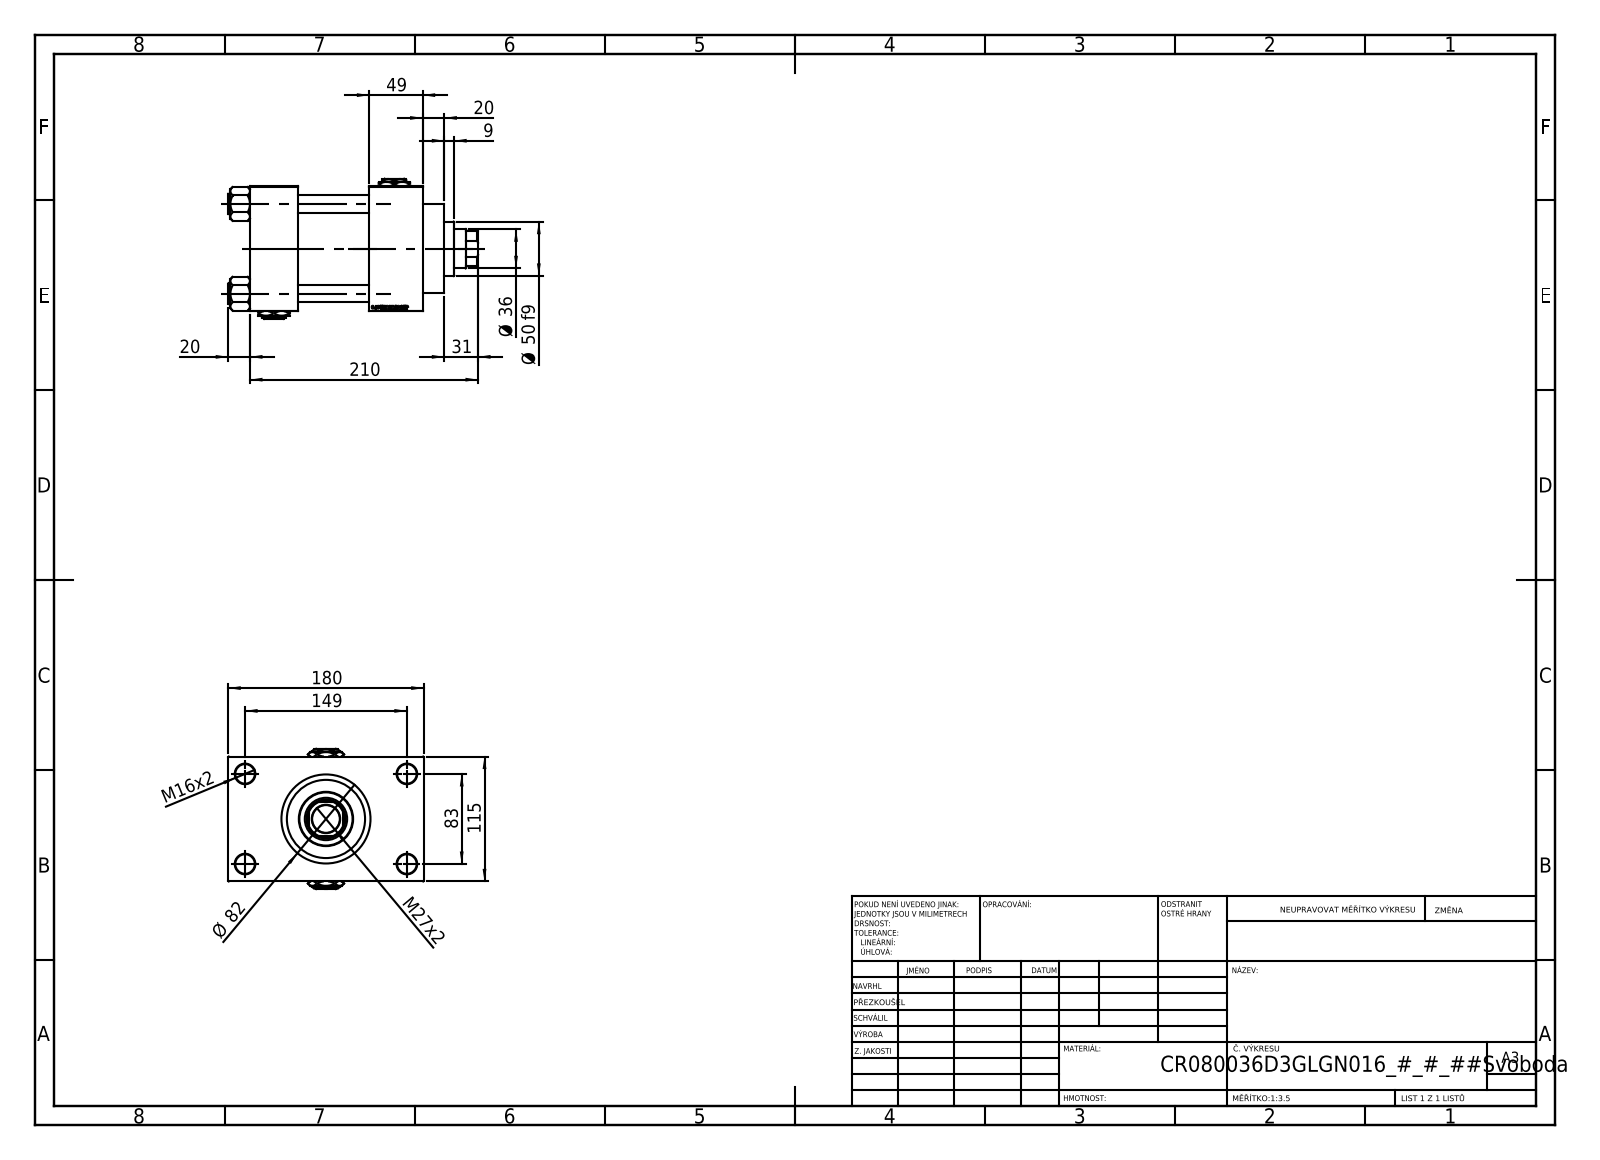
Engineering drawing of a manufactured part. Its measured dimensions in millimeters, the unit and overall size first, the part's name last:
Units: millimetres
Overall size (bounding box): 230 × 180 × 129
Round holes (diameter × count): ⌀16 ×4, ⌀18 ×4, ⌀7 ×2, ⌀26.44 ×2, ⌀35 ×2, ⌀25.5 ×1, ⌀36 ×1, ⌀39 ×1, ⌀61 ×1, ⌀72 ×1, ⌀80 ×1
Round bosses / shafts (diameter × count): ⌀19 ×4, ⌀86 ×1, ⌀82 ×1, ⌀50 ×1
Partial cylindrical surfaces — rounded edges, fillets, slot ends (radius × count): R17.5 ×1
Main face-to-face distances: 115, 66, 110, 49, 44, 159, 147.5, 32.5, 20, 69
Hole centre spacings: 33.15, 58.48, 82.7, 85.28, 89.24, 115.85, 142.43, 83
Volume: 2 005 000 mm³ · Surface area: 297 927 mm²
Bodies: 13 solids, 1236 faces (589 planar, 89 cylindrical, 558 other)
Part name (STEP PRODUCT): Zatka_pro_OIL_PORT; V215CR_D_TYCINKA; V215CR_VCP_D; V215CR_D_Body (+2 more)
STEP written by: SolidWorks 2019 (CONFIG_CONTROL_DESIGN)
